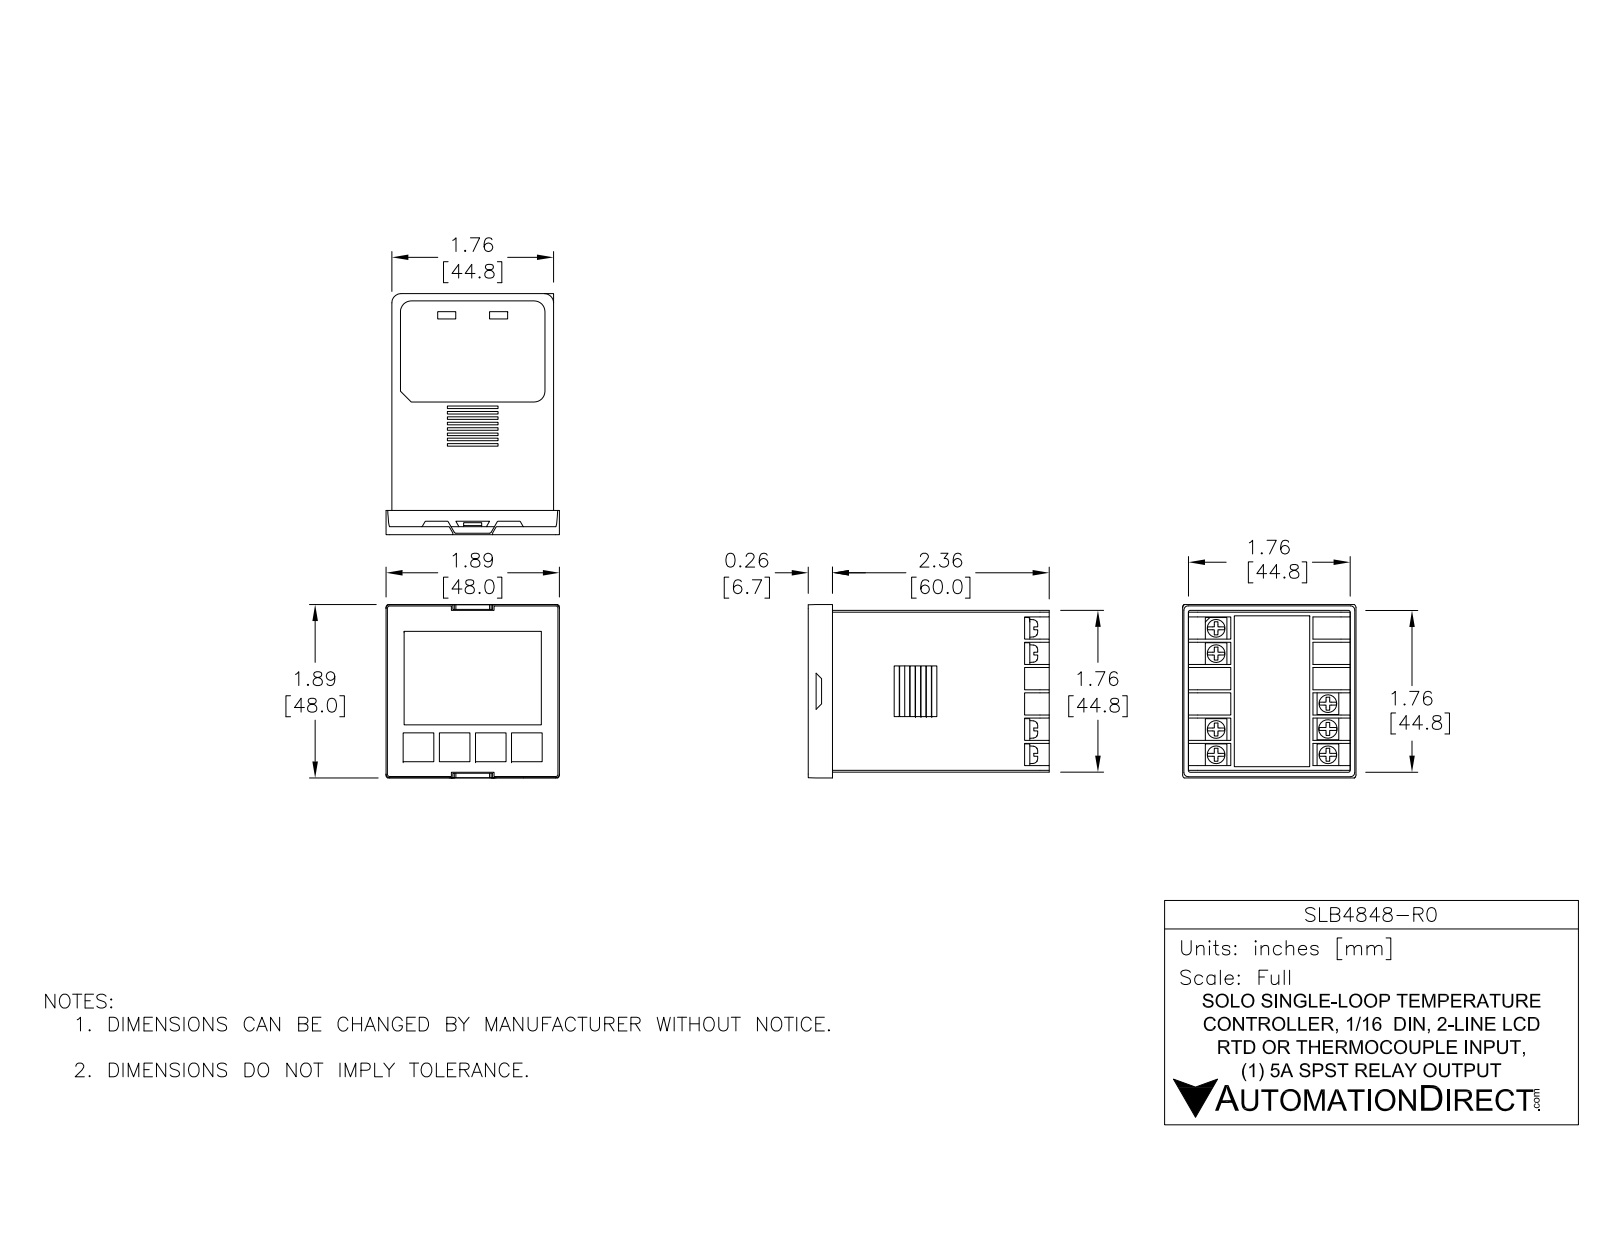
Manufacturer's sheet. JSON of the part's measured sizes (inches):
{"part_name": "SLB4848-R0", "step_written_by": "SolidWorks 2017 (AUTOMOTIVE_DESIGN)", "units": "inches", "bodies": {"solids": 5, "faces": 3364, "planar": 3117, "cylindrical": 141, "other": 106}, "overall_size": [2.628, 2.234, 1.89], "volume_in3": 7.68, "surface_area_in2": 46.55, "round_bosses_or_shafts": [[0.21, 2], [0.114, 2]], "partial_cylinders_radius": [[0.006, 36], [0.008, 8], [0.02, 6], [0.039, 6], [0.024, 4], [0.04, 4], [0.063, 4], [0.157, 4]], "face_to_face_distances": [1.762, 0.049, 1.813, 0.016, 1.746, 0.05, 1.763, 1.764, 1.763, 1.812]}
